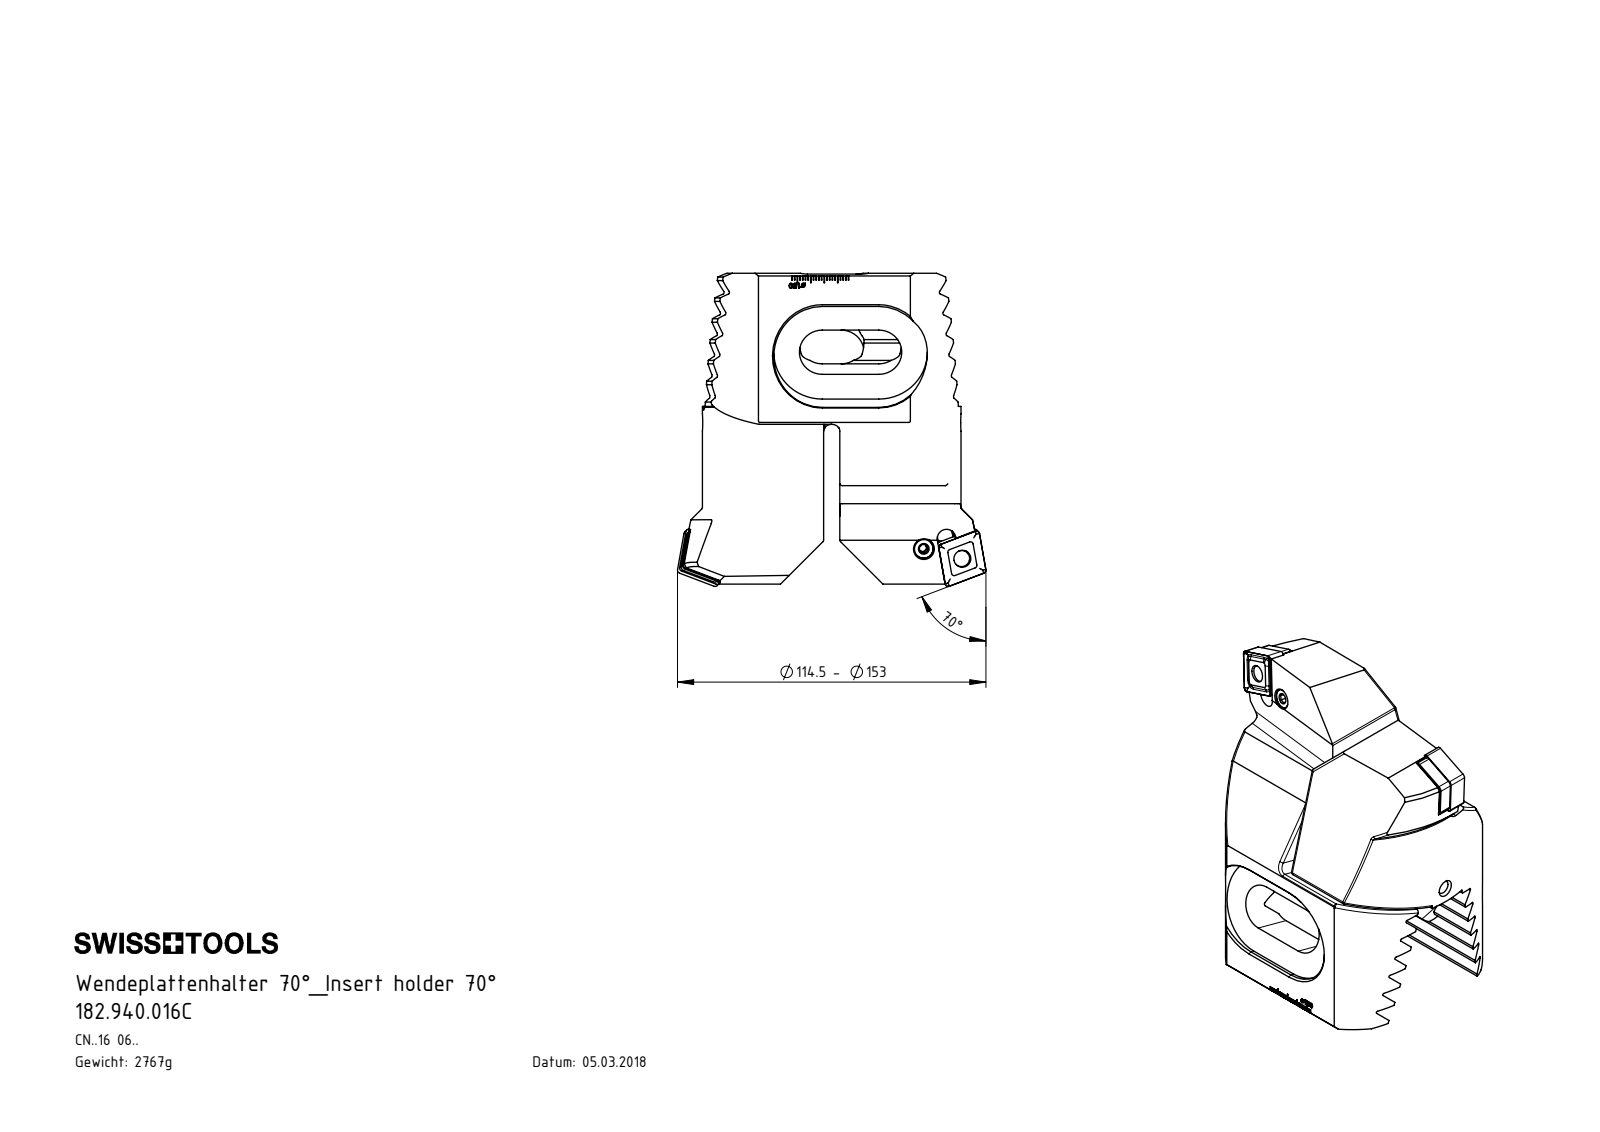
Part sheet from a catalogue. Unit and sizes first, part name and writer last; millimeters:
Units: millimetres
Overall size (bounding box): 116.2 × 114.5 × 75.2
Round holes (diameter × count): ⌀2 ×2, ⌀6.35 ×2, ⌀7 ×2, ⌀8.05 ×2, ⌀8.4 ×2, ⌀5 ×1
Round bosses / shafts (diameter × count): ⌀6 ×3, ⌀8 ×2, ⌀7.9 ×2, ⌀6.4 ×2, ⌀3.55 ×2, ⌀4 ×1
Partial cylindrical surfaces — rounded edges, fillets, slot ends (radius × count): R1 ×16, R0.58 ×12, R1.2 ×8, R1.5 ×8, R3 ×6, R3.5 ×6, R0.3 ×4, R8.5 ×4
Main face-to-face distances: 6.93, 13.86, 20.79, 27.71, 13.19, 6, 20.78, 1.59, 13.85, 27.72
Hole centre spacings: 14.78, 15, 25, 48.3
Volume: 351 479 mm³ · Surface area: 70 327 mm²
Bodies: 14 solids, 962 faces (536 planar, 168 cylindrical, 258 other)
Part name (STEP PRODUCT): 182.940.016C; Z72-ER3.001.030; CNMG160612; WCE-ER2.101.004_A (+5 more)
STEP written by: SolidWorks 2017 (CONFIG_CONTROL_DESIGN)
